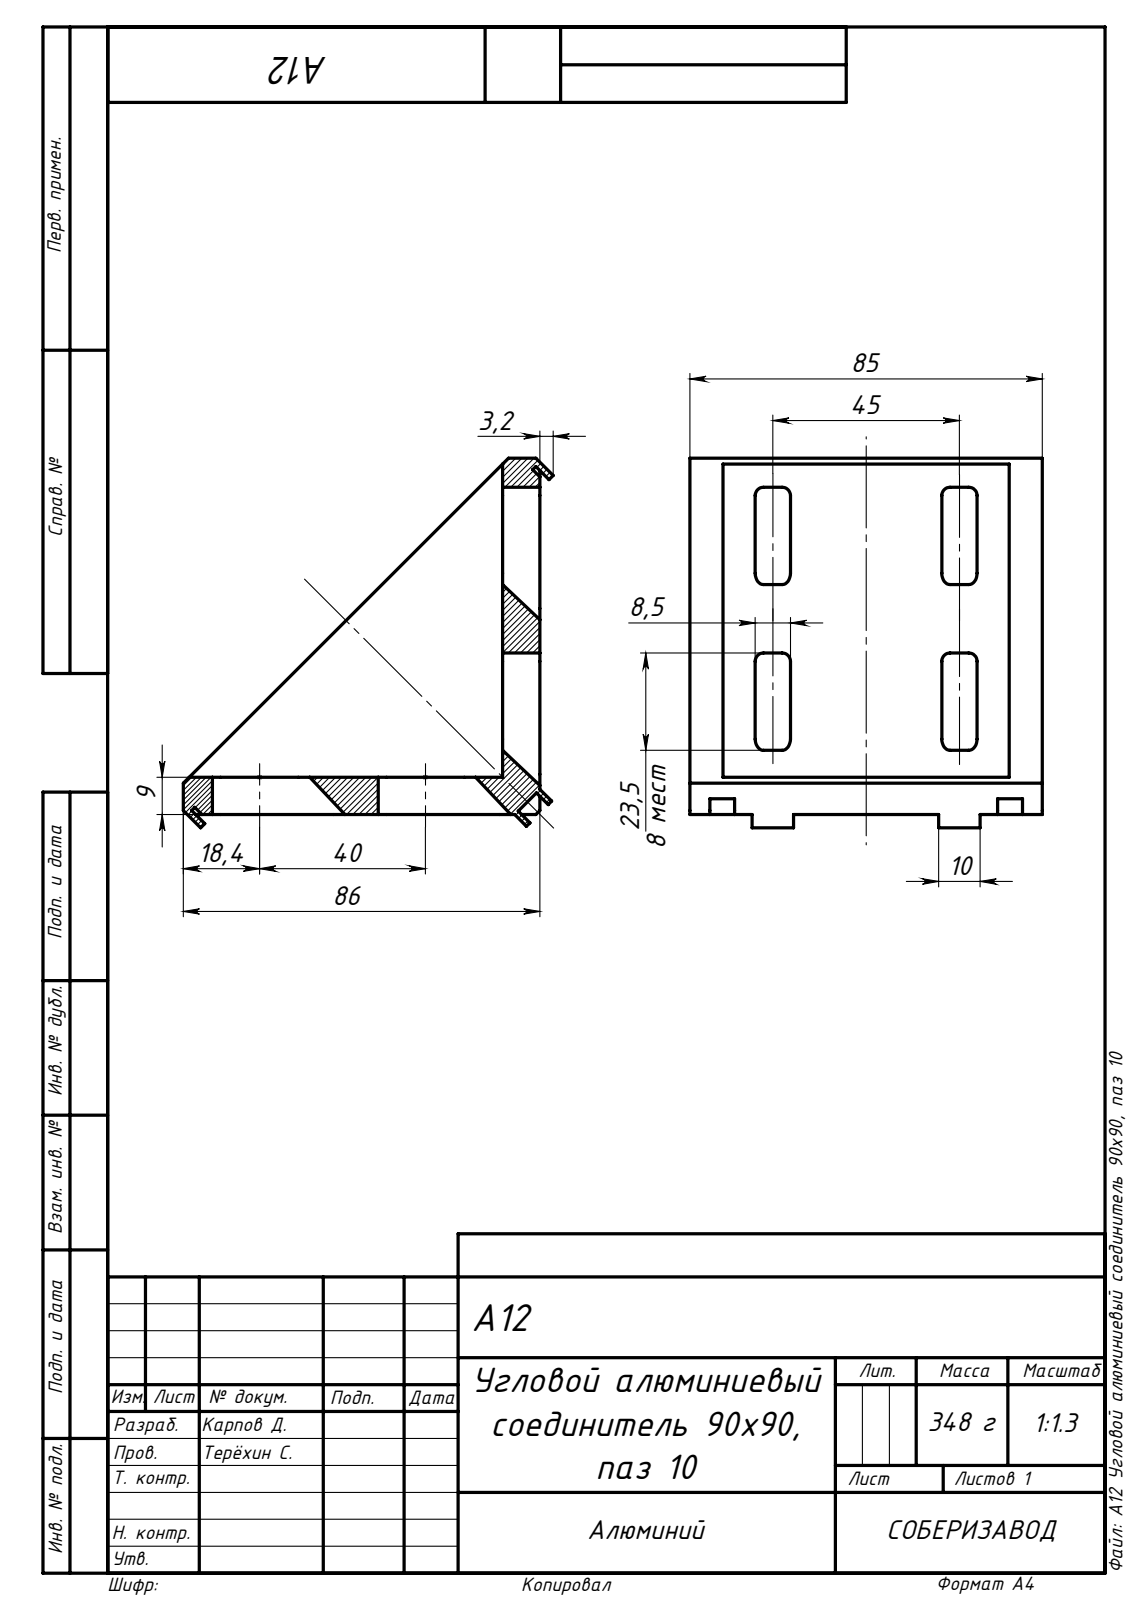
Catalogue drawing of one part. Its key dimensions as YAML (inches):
part_name: "A12 Угловой алюминиевый соединитель 90х90, паз 10"
step_written_by: "SolidWorks 2021 (AUTOMOTIVE_DESIGN)"
units: inches
bodies: {solids: 1, faces: 244, planar: 172, cylindrical: 72, other: 0}
overall_size: [3.511, 3.511, 3.346]
volume: 8.529
surface_area: 72.91
partial_cylinders:
  - {radius: 0.039, count: 40}
  - {radius: 0.079, count: 32}
face_to_face_distances: [3.031, 0.354, 0.315, 0.102, 0.252, 3.346, 2.717, 1.772, 0.62, 2.726]
